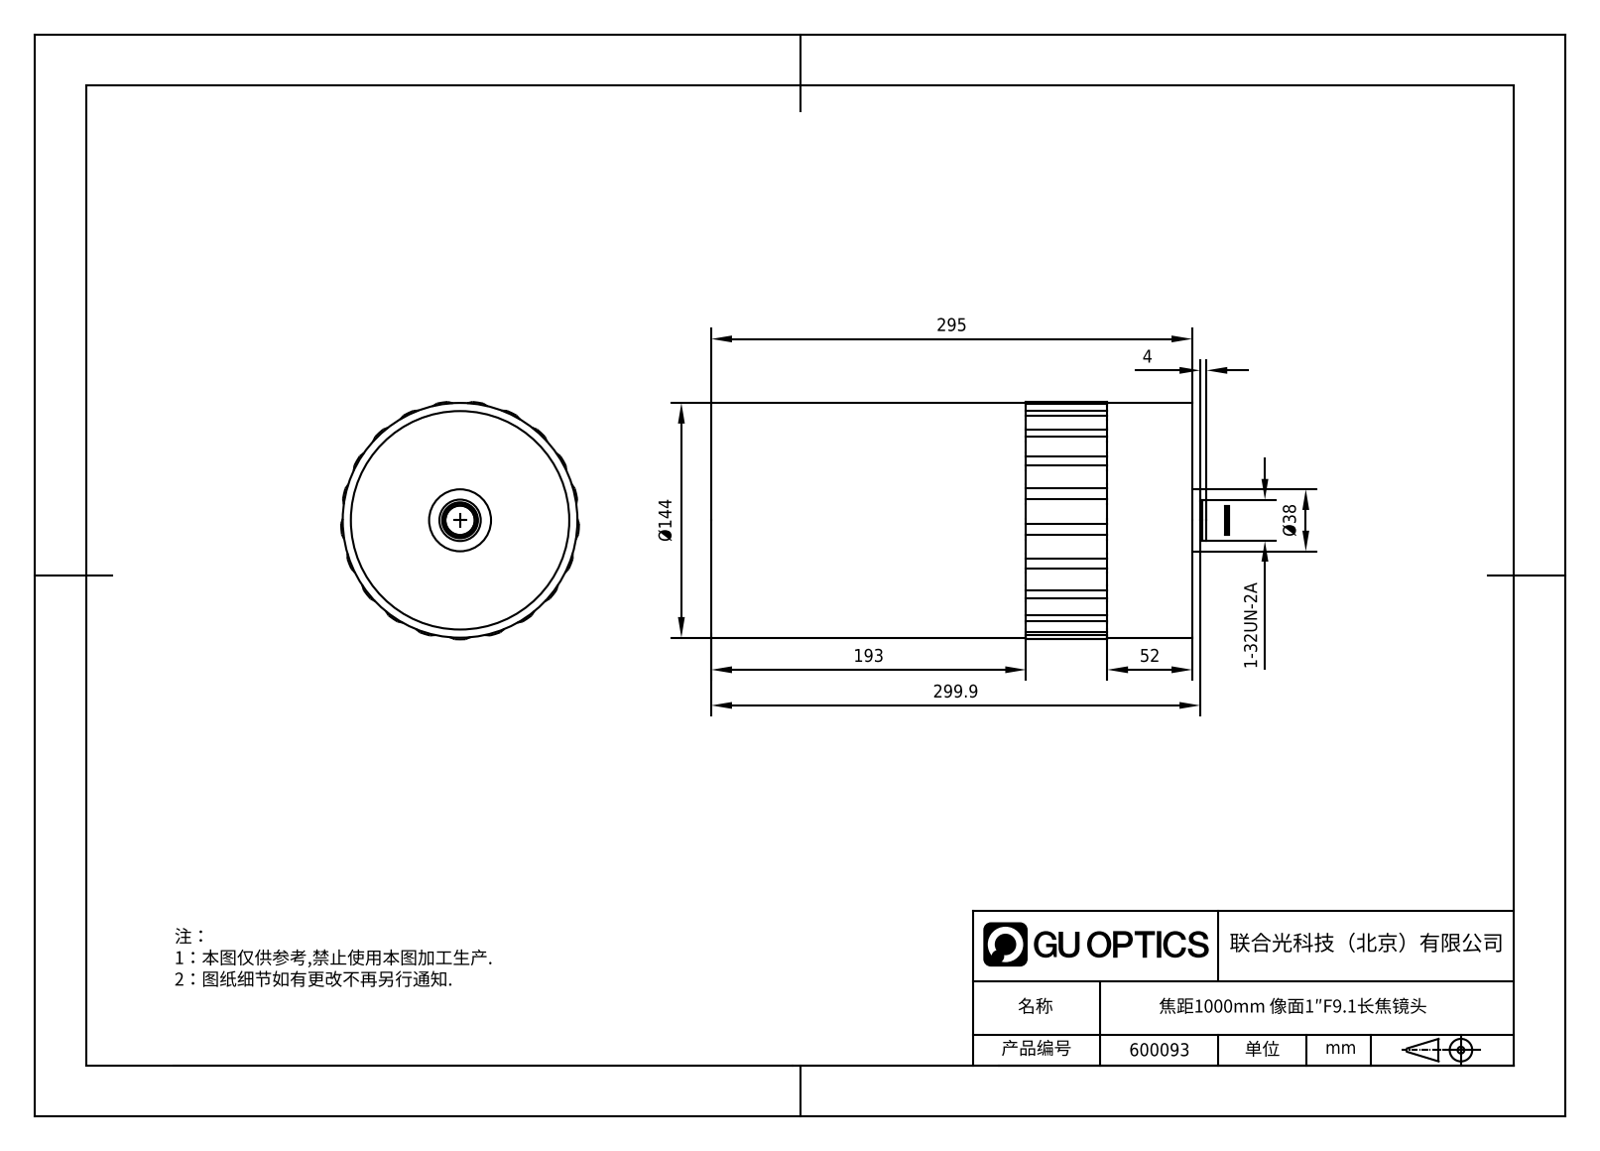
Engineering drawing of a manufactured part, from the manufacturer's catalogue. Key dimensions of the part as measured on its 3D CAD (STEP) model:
Part name (STEP PRODUCT): 600093
STEP written by: SolidWorks 2020 (CONFIG_CONTROL_DESIGN)
Units: millimetres
Bodies: 11 solids, 111 faces (33 planar, 73 cylindrical, 5 other)
Overall size (bounding box): 317.42 × 145.94 × 145.6
Volume: 1 245 000 mm³ · Surface area: 490 418 mm²
Round holes (diameter × count): ⌀22 ×1, ⌀33 ×1, ⌀36 ×1, ⌀115 ×1, ⌀118 ×1, ⌀120 ×1, ⌀126 ×1, ⌀130 ×1, ⌀134 ×1, ⌀136 ×1, ⌀138 ×1, ⌀140 ×1
Round bosses / shafts (diameter × count): ⌀144 ×1, ⌀120.7 ×1, ⌀38 ×1, ⌀34.69 ×1, ⌀25.4 ×1, ⌀24 ×1, ⌀20.22 ×1, ⌀18.1 ×1
Partial cylindrical surfaces — rounded edges, fillets, slot ends (radius × count): R27 ×21, R73 ×1
Main face-to-face distances: 4, 8, 277.45, 281.45, 285.45, 183.45, 94, 98, 102, 268.95
